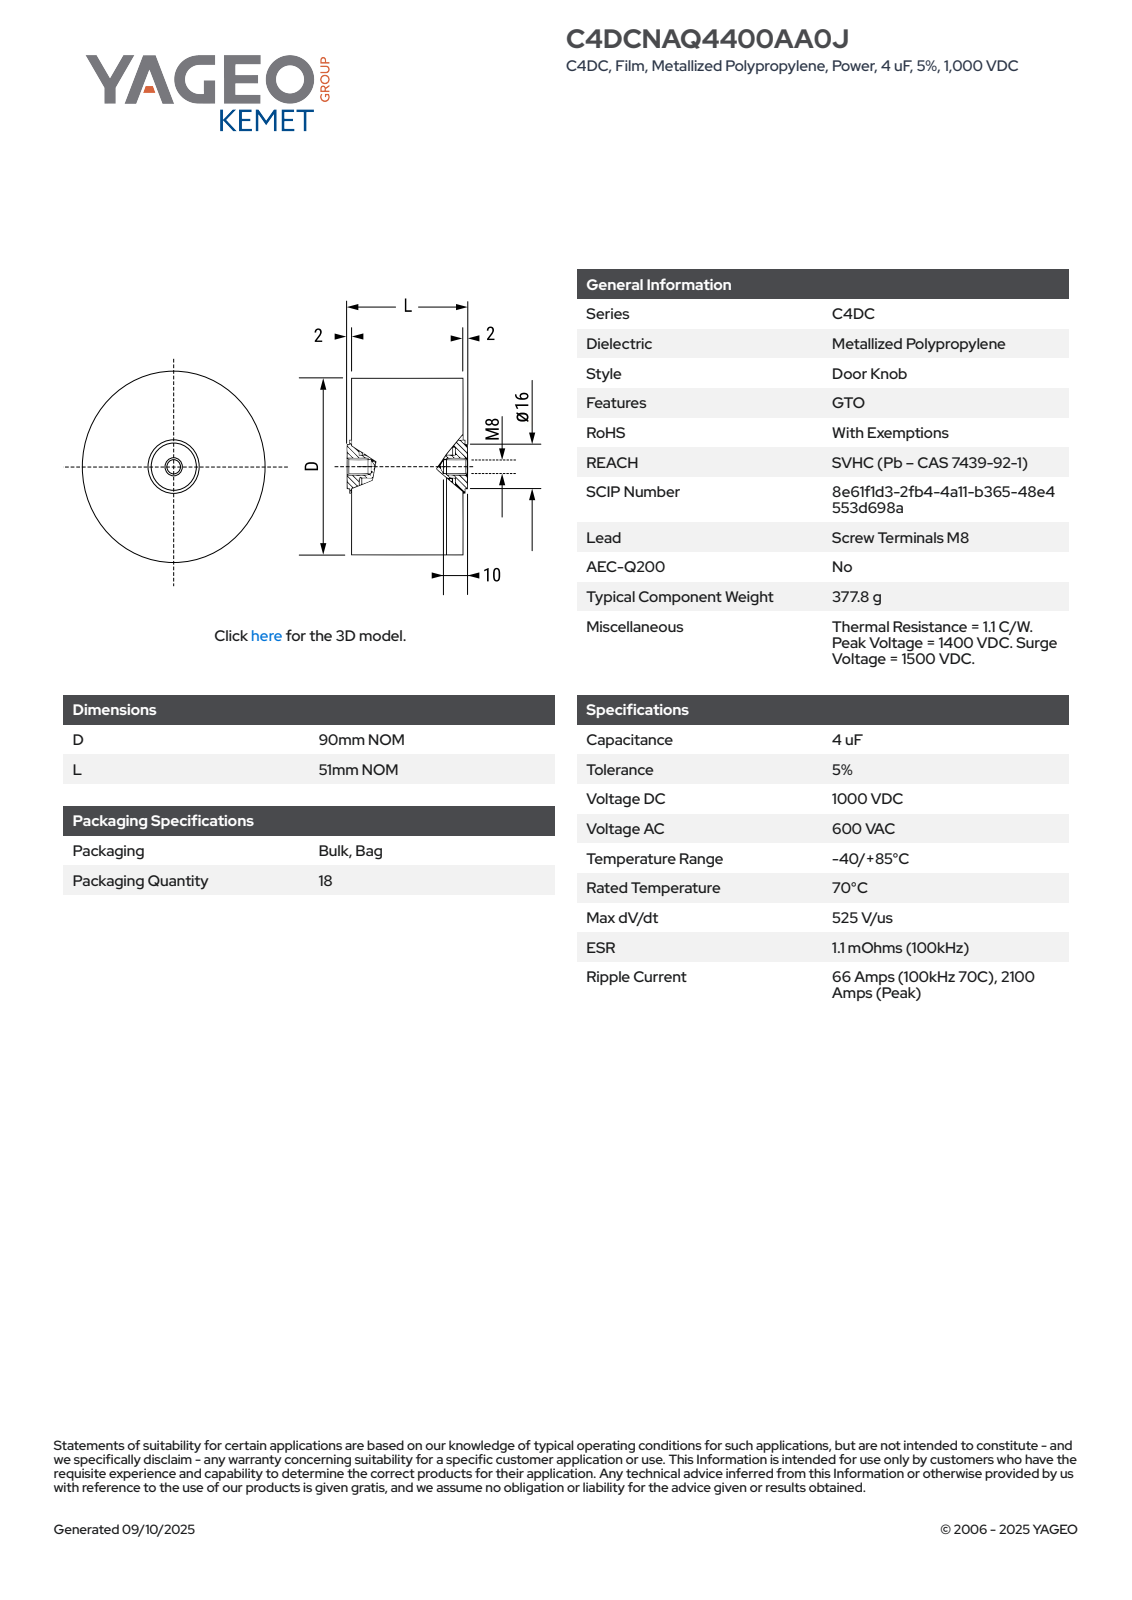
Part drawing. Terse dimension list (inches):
name: CFP_KD_90x51_D90L51
written by: SolidWorks 2014 (AUTOMOTIVE_DESIGN)
unit: in
bodies: 1 solid, 84 faces (30 planar, 23 cylindrical, 31 other)
size: 3.543 × 3.543 × 2.008
volume: 18.23 in³; area: 41.4 in²
holes: 1× ⌀0.315
bosses: 1× ⌀3.543, 1× ⌀0.63, 1× ⌀0.531
rounds: 1× R1.771
face distances: 1.85, 0.079, 1.929, 0.026, 1.982, 0.053, 1.904, 0.394, 1.614, 0.368
